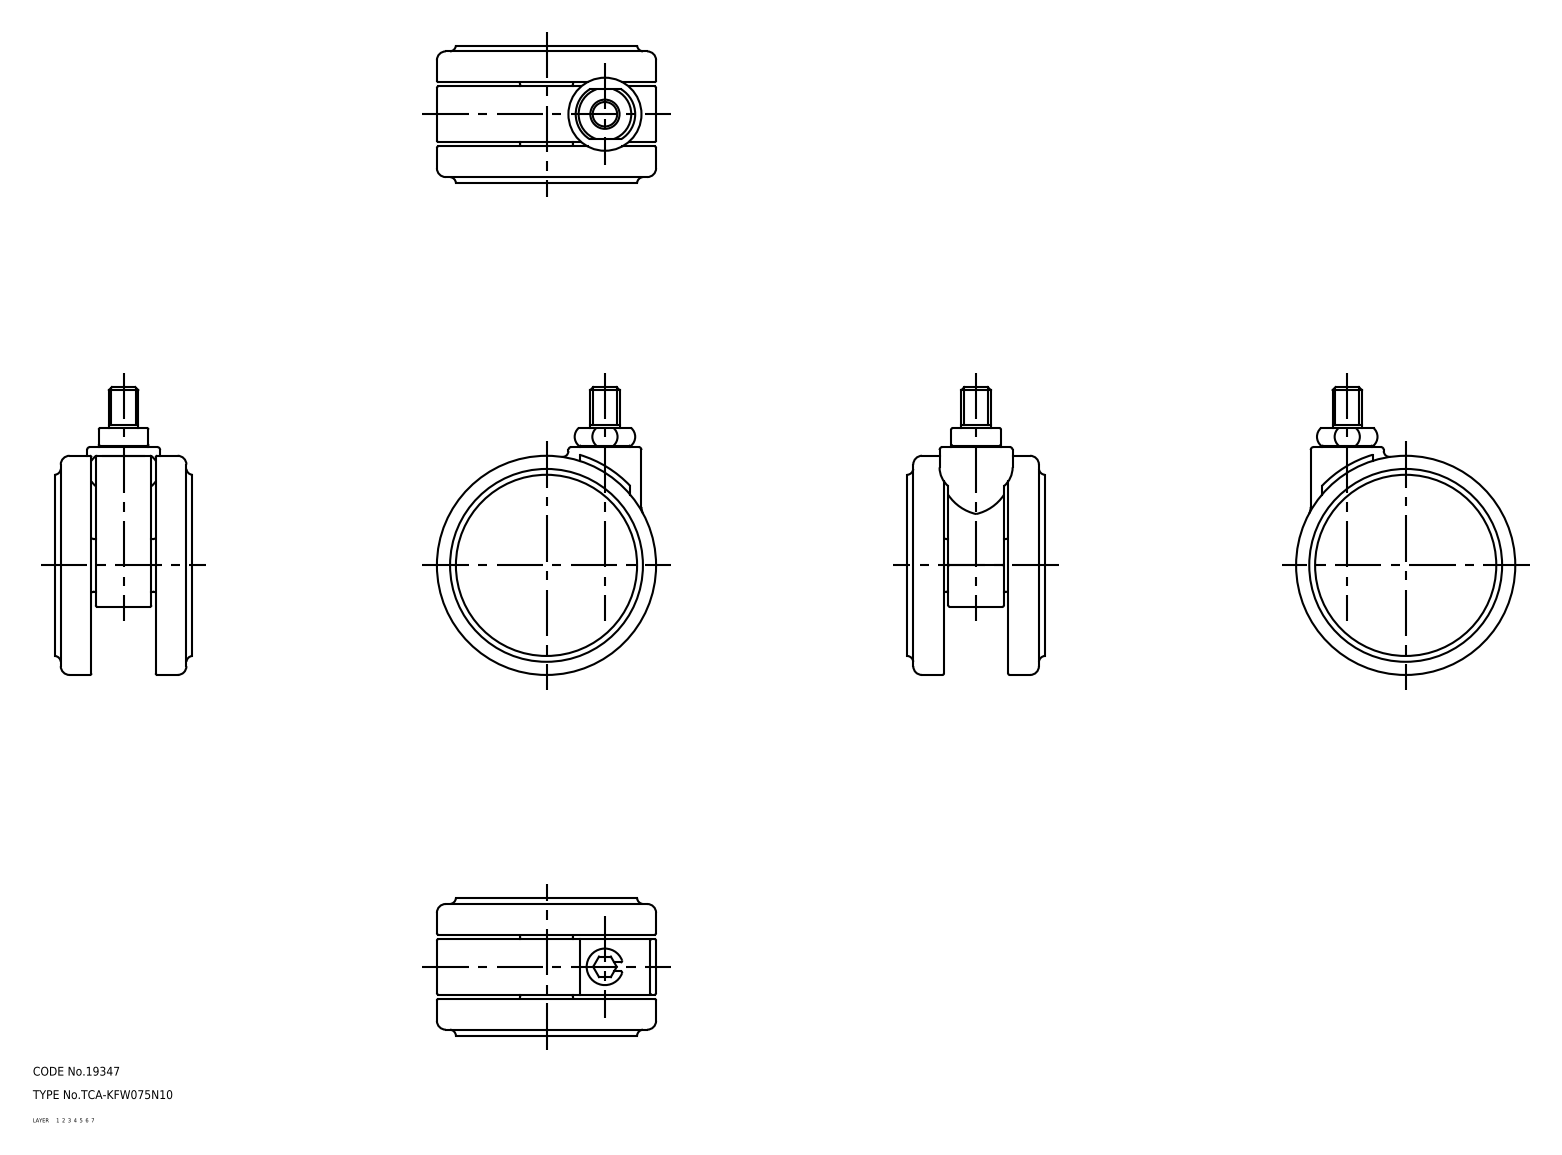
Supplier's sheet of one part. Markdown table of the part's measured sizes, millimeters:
| quantity | value |
| --- | --- |
| part name | TCA_KFW075N10; main shaft; wheel; wheel_mr |
| STEP written by | SolidWorks 2015 (AUTOMOTIVE_DESIGN) |
| units | millimeters |
| bodies | 4 solids, 126 faces (35 planar, 45 cylindrical, 46 other) |
| overall size | 98.5 × 75 × 47 |
| volume | 159 819 mm³ |
| surface area | 36 885 mm² |
| round holes (diameter × count) | 6 × 1, 43 × 1 |
| round bosses / shafts (diameter × count) | 75 × 1, 25 × 1, 18 × 1, 17 × 1, 12.5 × 1, 10 × 1 |
| partial cylindrical surfaces (radius × count) | 0.5 × 13, 1 × 1, 2.89 × 1, 14.41 × 1, 39.5 × 1 |
| main face-to-face distances | 14, 33, 1.5, 20.5, 12.5, 34.5, 47, 19, 22, 25 |
